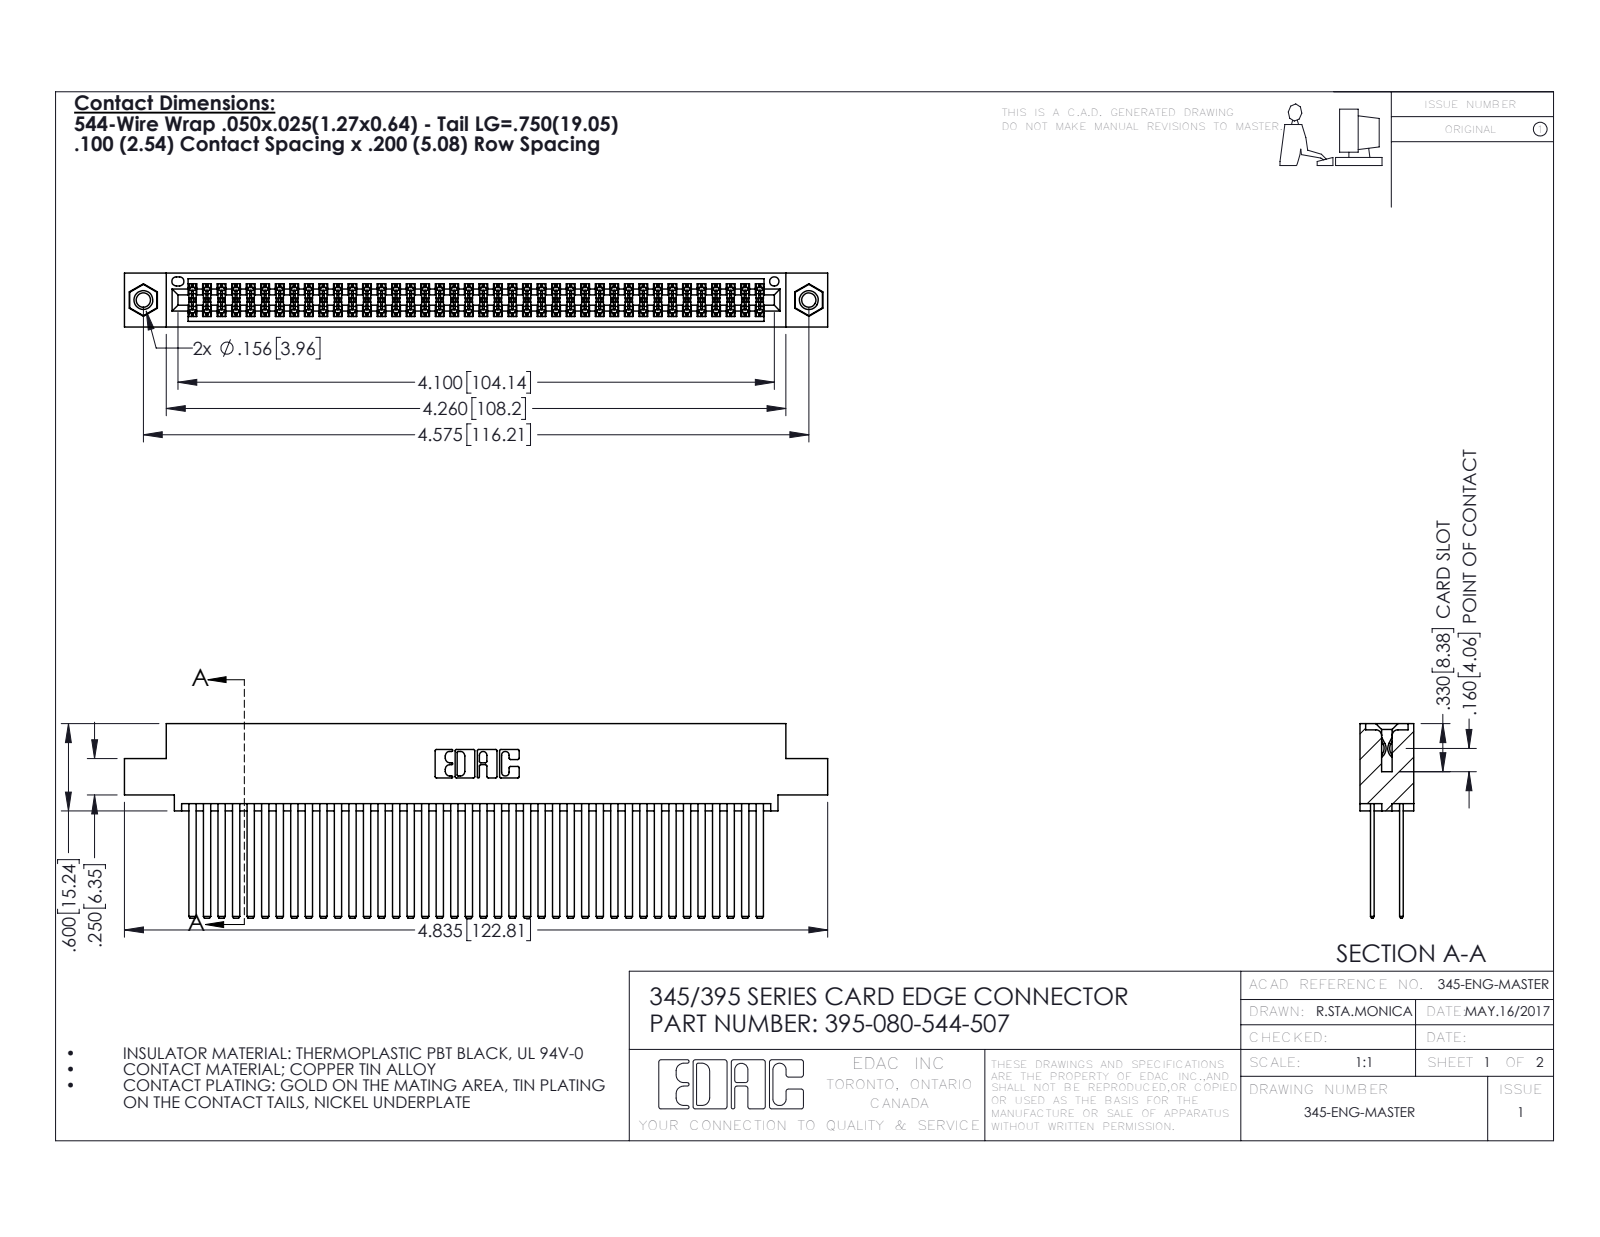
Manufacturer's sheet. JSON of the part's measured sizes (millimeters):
{"part_name": "395-080-544-507; 345-292-001_345-293-144; 345-250-001_345-250-005-103; 345 Part_0.110 Offset - 0.156 Dia-TI", "step_written_by": "SolidWorks 2016 (CONFIG_CONTROL_DESIGN)", "units": "millimeters", "bodies": {"solids": 83, "faces": 3710, "planar": 2436, "cylindrical": 1258, "other": 16}, "overall_size": [122.8, 34, 9.4], "volume_mm3": 12900, "surface_area_mm2": 22500, "round_holes": [[2.5, 2], [3.2, 2], [4, 2], [1.6, 1]], "round_bosses_or_shafts": [[3.9, 2]], "partial_cylinders_radius": [[0.2, 120], [0.3, 22], [0.2, 6], [0.8, 6], [0.7, 3], [0.4, 2], [0.5, 2], [0.6, 2]], "face_to_face_distances": [5.1, 0.6, 1.8, 2.5, 6.9, 7.6, 5.7, 4.4, 9.4, 1.3], "hole_center_spacings": [6.9, 110.2, 116.2]}
